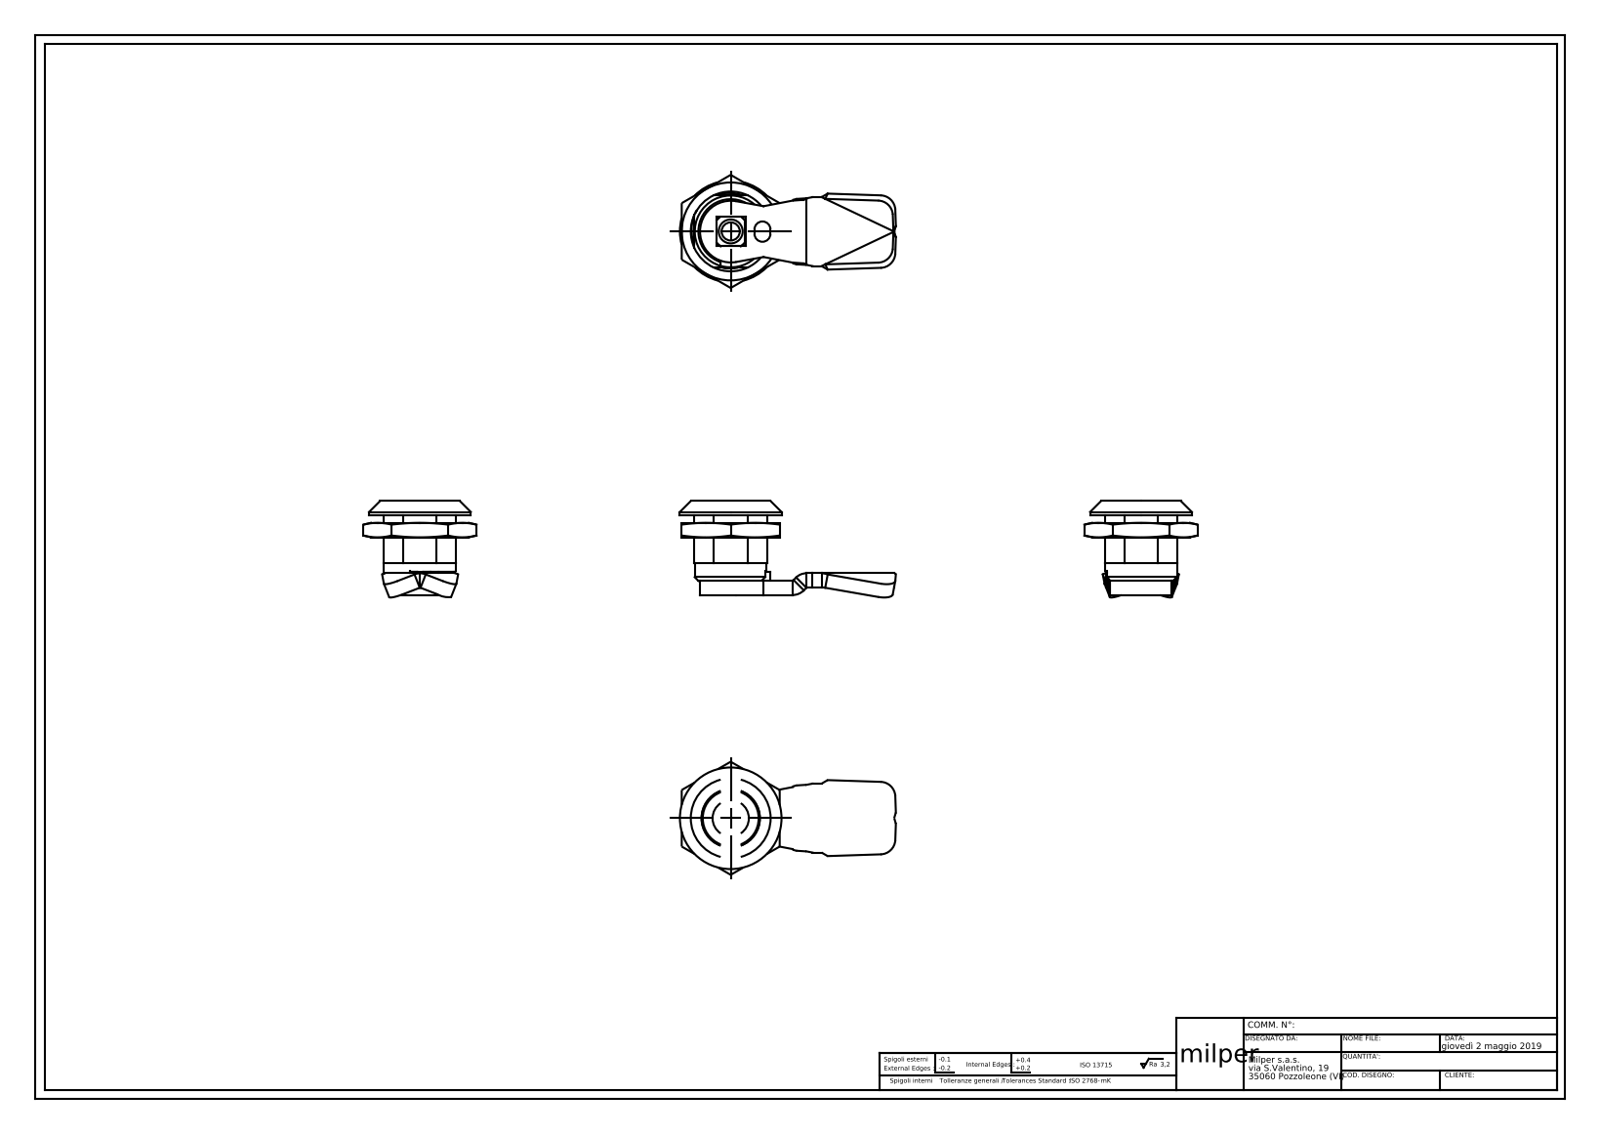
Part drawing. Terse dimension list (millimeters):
name: 1.26.21.0003-serratura-asportabili-Milper
written by: SolidWorks 2019 (CONFIG_CONTROL_DESIGN)
unit: mm
bodies: 0 solids, 455 faces (252 planar, 120 cylindrical, 83 other)
size: 59.51 × 57.99 × 40
holes: 1× ⌀5, 1× ⌀5.8, 1× ⌀6, 1× ⌀10, 1× ⌀16.1, 1× ⌀20.38
bosses: 1× ⌀28, 1× ⌀22, 1× ⌀19.8, 1× ⌀16, 1× ⌀12.8, 1× ⌀9.9, 1× ⌀9, 1× ⌀6
rounds: 21× R0.5, 9× R4, 6× R1, 2× R2.2, 2× R6, 2× R20.23, 1× R0.4, 1× R0.53
face distances: 2, 4, 6, 15.9, 19.9, 13.9, 17.9, 11.9, 21.9, 2.5
